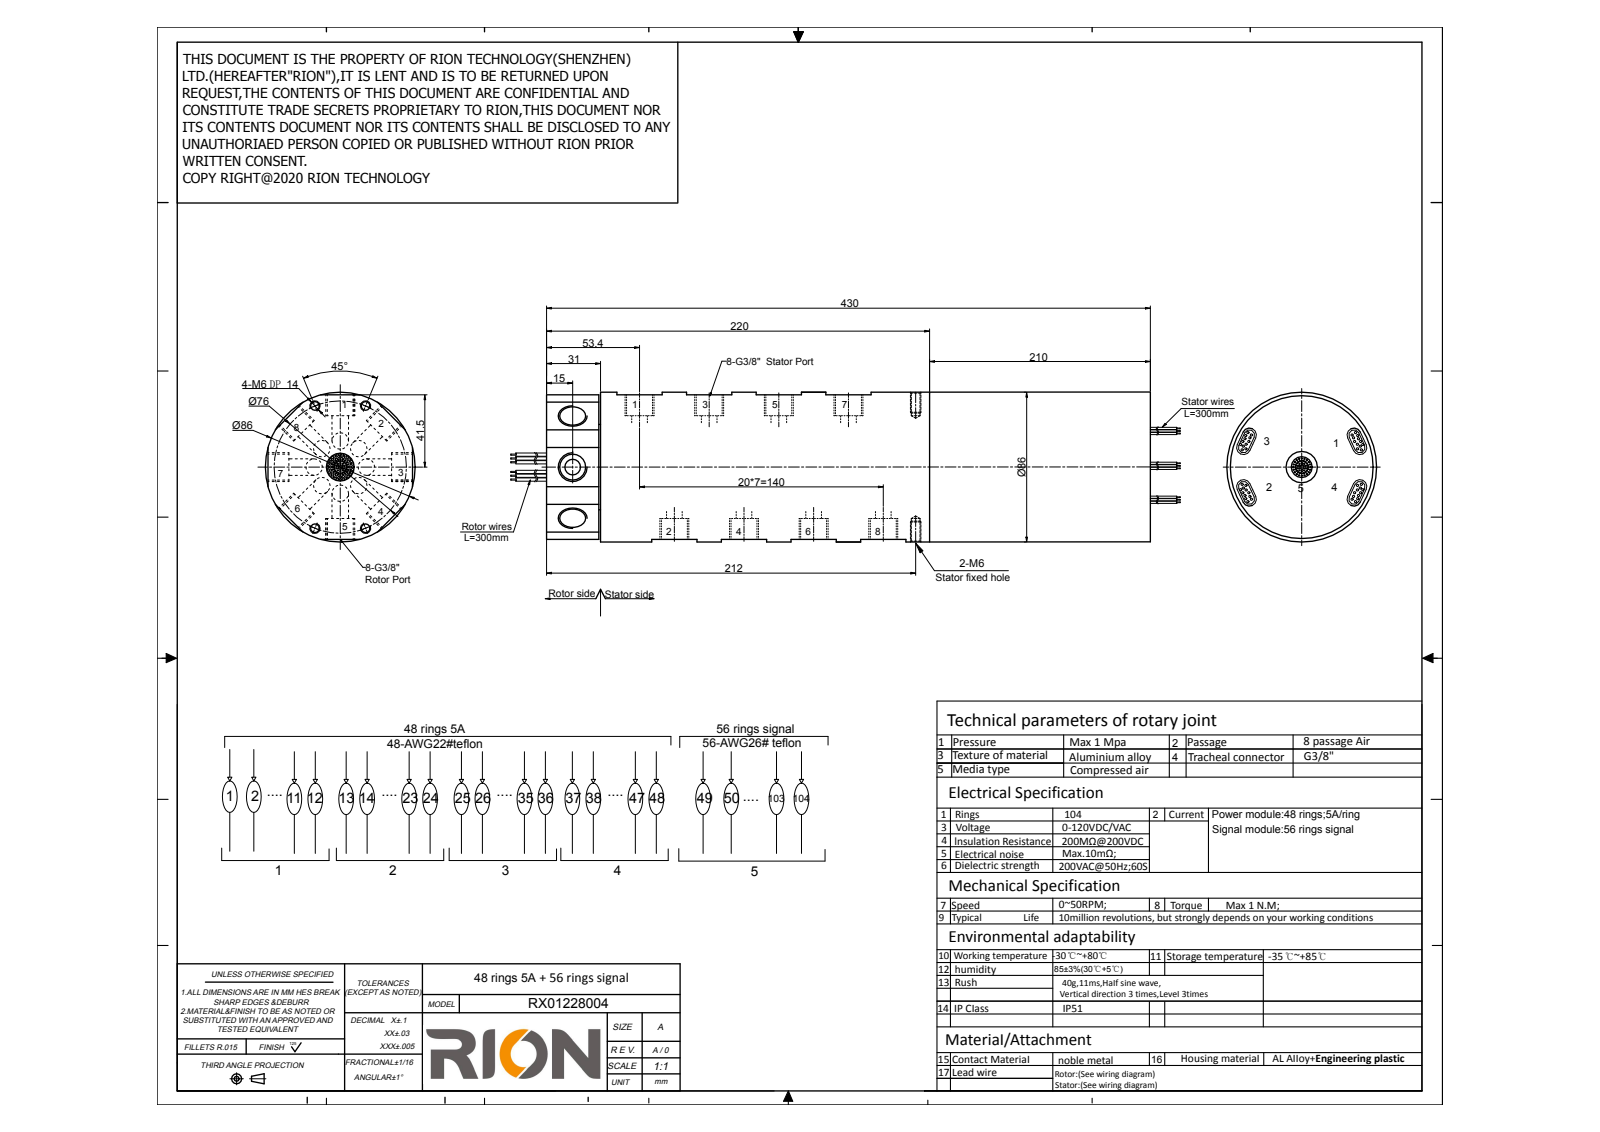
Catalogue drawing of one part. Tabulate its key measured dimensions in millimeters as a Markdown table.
| quantity | value |
| --- | --- |
| part name | MK83S-P4805-S56(B2900) |
| STEP written by | SolidWorks 2014 (CONFIG_CONTROL_DESIGN) |
| units | millimeters |
| bodies | 1 solid, 852 faces (276 planar, 530 cylindrical, 46 other) |
| overall size | 528.5 × 86 × 86 |
| volume | 2 427 000 mm³ |
| surface area | 296 616 mm² |
| round holes (diameter × count) | 9 × 14, 15.25 × 14, 5 × 5, 16 × 1, 82 × 1 |
| round bosses / shafts (diameter × count) | 1.3 × 96, 0.8 × 77, 86 × 1, 81.8 × 1, 49 × 1 |
| partial cylindrical surfaces (radius × count) | 3 × 8 |
| main face-to-face distances | 430, 399, 30, 1, 31, 400, 83, 82.98, 26.5, 56.5 |
| hole center spacings | 20, 40, 60, 24.82, 38, 52.18, 80, 100 |
